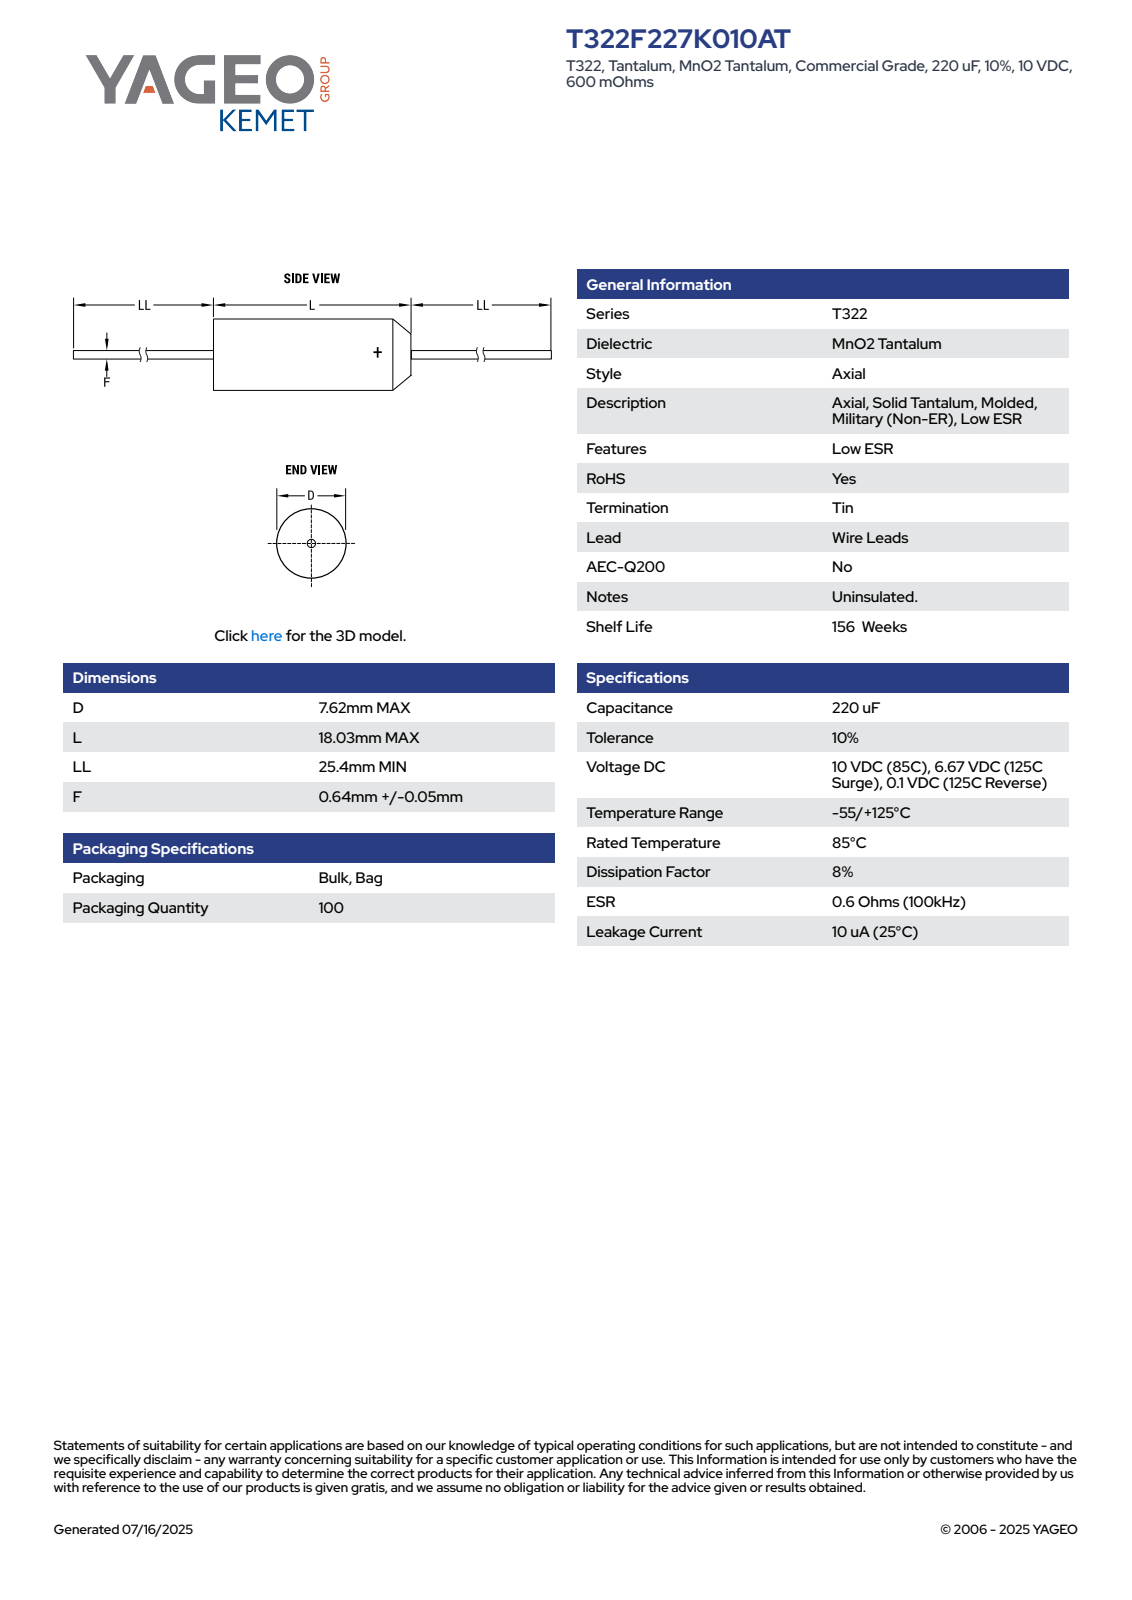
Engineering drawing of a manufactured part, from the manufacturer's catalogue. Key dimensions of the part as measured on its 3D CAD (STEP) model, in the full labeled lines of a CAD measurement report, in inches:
Part name (STEP PRODUCT): CTAM_D7.62L18.03LL25.4F0.69
STEP written by: SolidWorks 2020 (AUTOMOTIVE_DESIGN)
Units: inches
Bodies: 1 solid, 102 faces (38 planar, 25 cylindrical, 39 other)
Overall size (bounding box): 2.71 × 0.3 × 0.3
Volume: 0.051 in³ · Surface area: 0.964 in²
Round bosses / shafts (diameter × count): ⌀0.3 ×1, ⌀0.027 ×1
Partial cylindrical surfaces — rounded edges, fillets, slot ends (radius × count): R0.15 ×1
Main face-to-face distances: 0.71, 1, 1.71, 2.71, 1.647, 0.647, 0.063, 1.063, 1.643, 0.643
